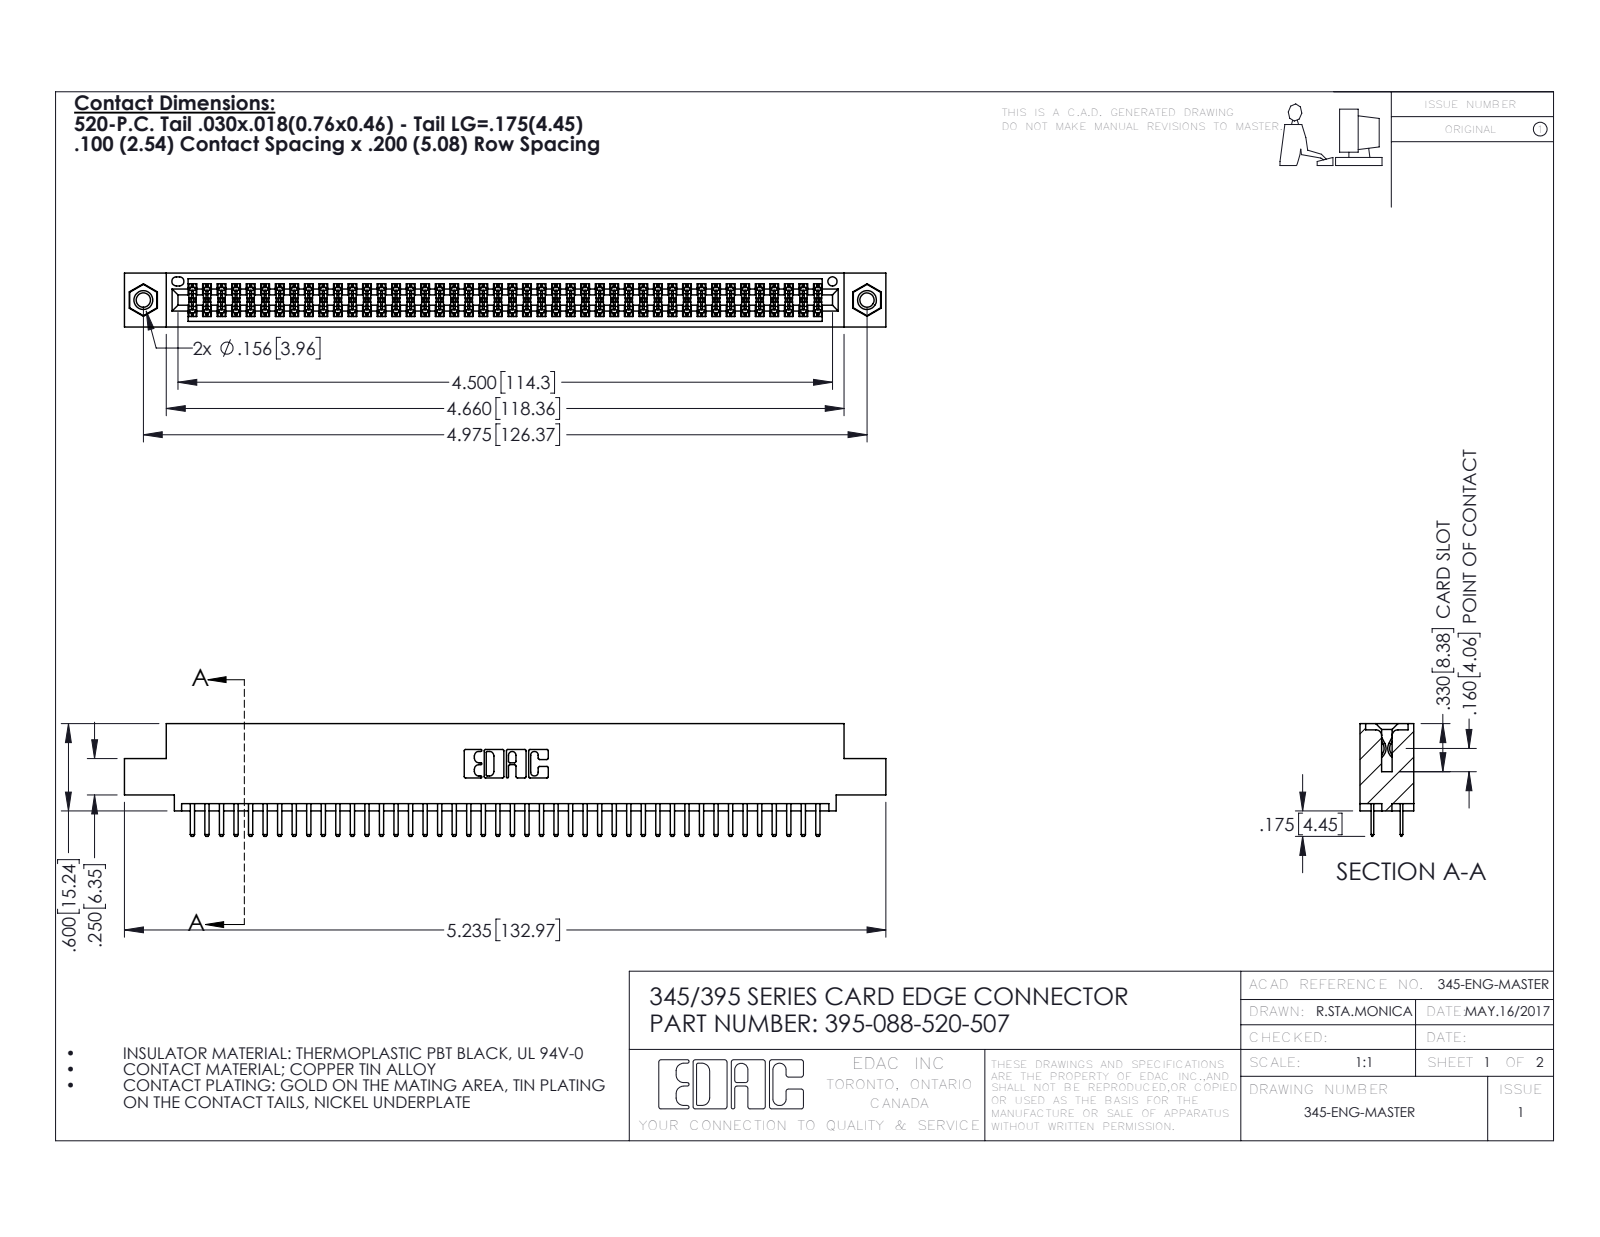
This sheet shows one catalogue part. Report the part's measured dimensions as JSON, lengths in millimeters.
{"part_name": "345-250-001_345-250-005-103; 345 Part_0.110 Offset - 0.156 Dia-TI; 395-088-520-507; 345-292-001_345-293-120", "step_written_by": "SolidWorks 2016 (CONFIG_CONTROL_DESIGN)", "units": "millimeters", "bodies": {"solids": 91, "faces": 4942, "planar": 3196, "cylindrical": 1730, "other": 16}, "overall_size": [133, 19.7, 9.4], "volume_mm3": 12800, "surface_area_mm2": 19010, "round_holes": [[2.5, 2], [3.2, 2], [4, 2], [1.6, 1]], "round_bosses_or_shafts": [[3.9, 2]], "partial_cylinders_radius": [[0.2, 132], [0.3, 92], [0.3, 22], [0.2, 6], [0.8, 6], [0.7, 3], [0.4, 2], [0.5, 2]], "face_to_face_distances": [1.8, 7.6, 5.1, 9.4, 2.5, 6.9, 0.6, 5.7, 0.6, 1.8], "hole_center_spacings": [6.9, 120.4, 126.4]}
